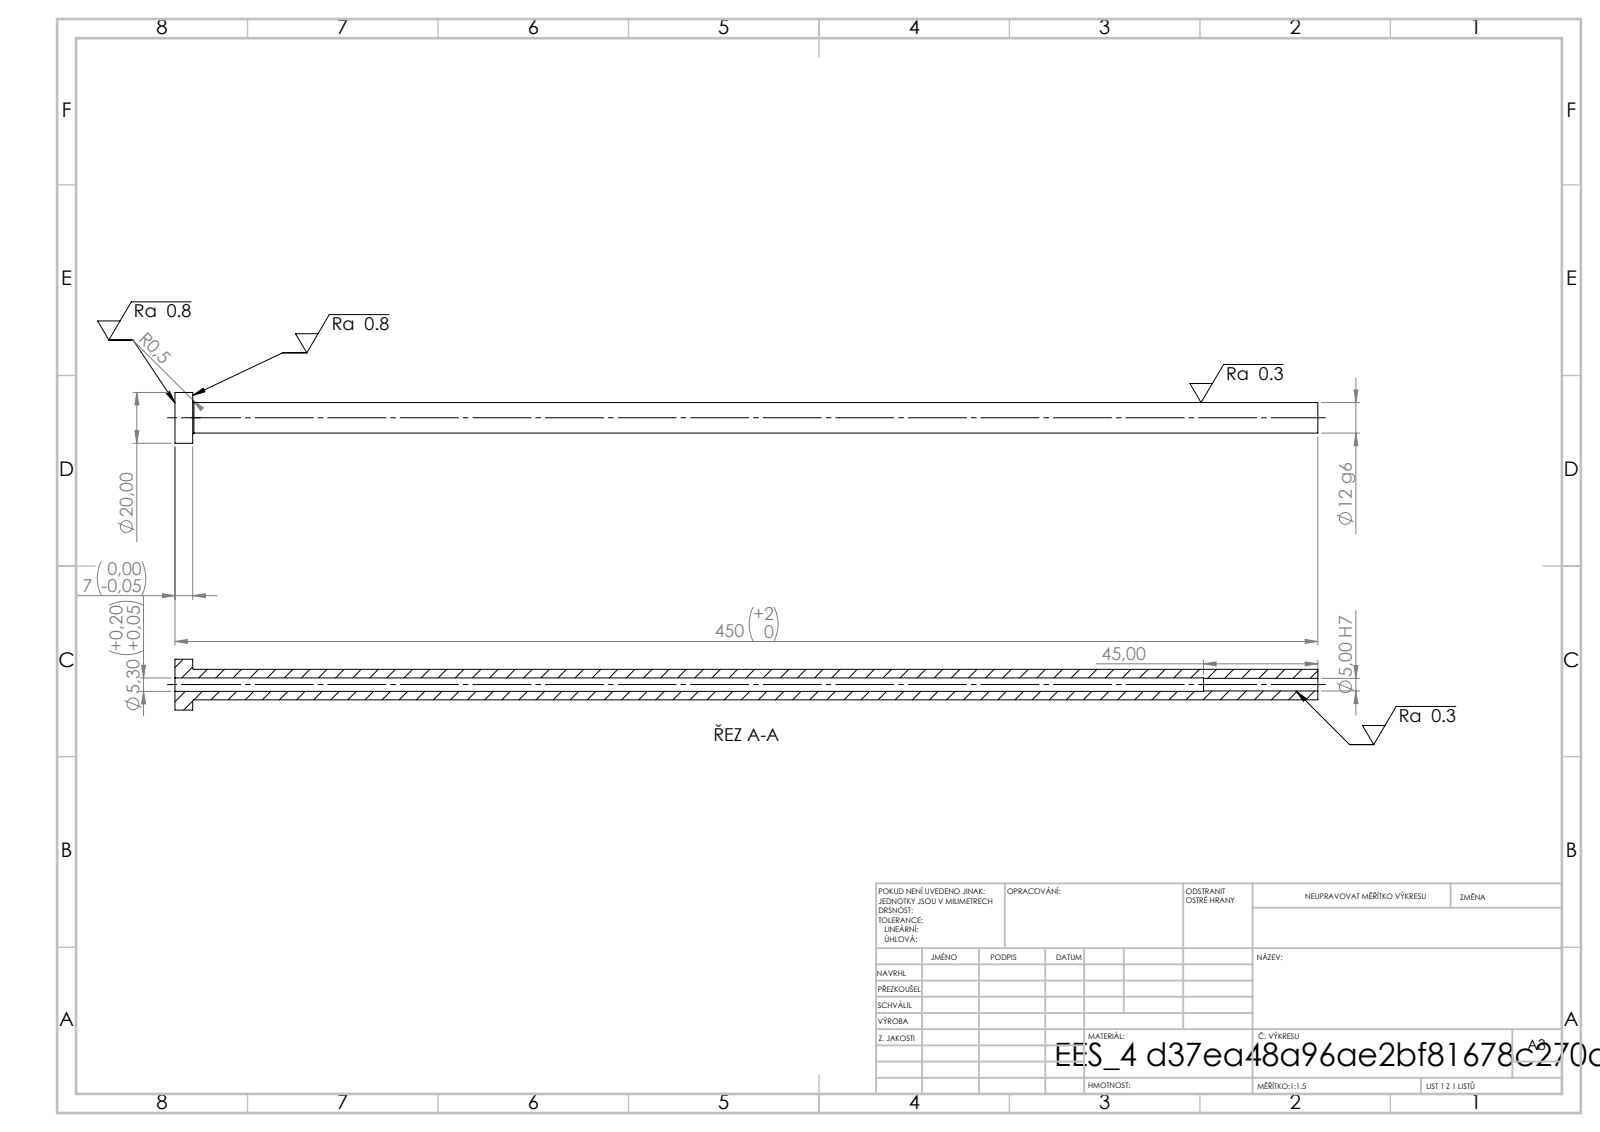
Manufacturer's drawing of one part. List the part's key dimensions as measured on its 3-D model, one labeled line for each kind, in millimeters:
STEP written by: SolidWorks 2019 (CONFIG_CONTROL_DESIGN)
Units: millimetres
Bodies: 1 solid, 14 faces (4 planar, 8 cylindrical, 2 other)
Overall size (bounding box): 450 × 20 × 20
Volume: 42 485 mm³ · Surface area: 25 172 mm²
Round holes (diameter × count): ⌀5 ×1, ⌀5.3 ×1
Round bosses / shafts (diameter × count): ⌀20 ×1, ⌀12 ×1
Main face-to-face distances: 7, 450, 443, 405, 398, 45
